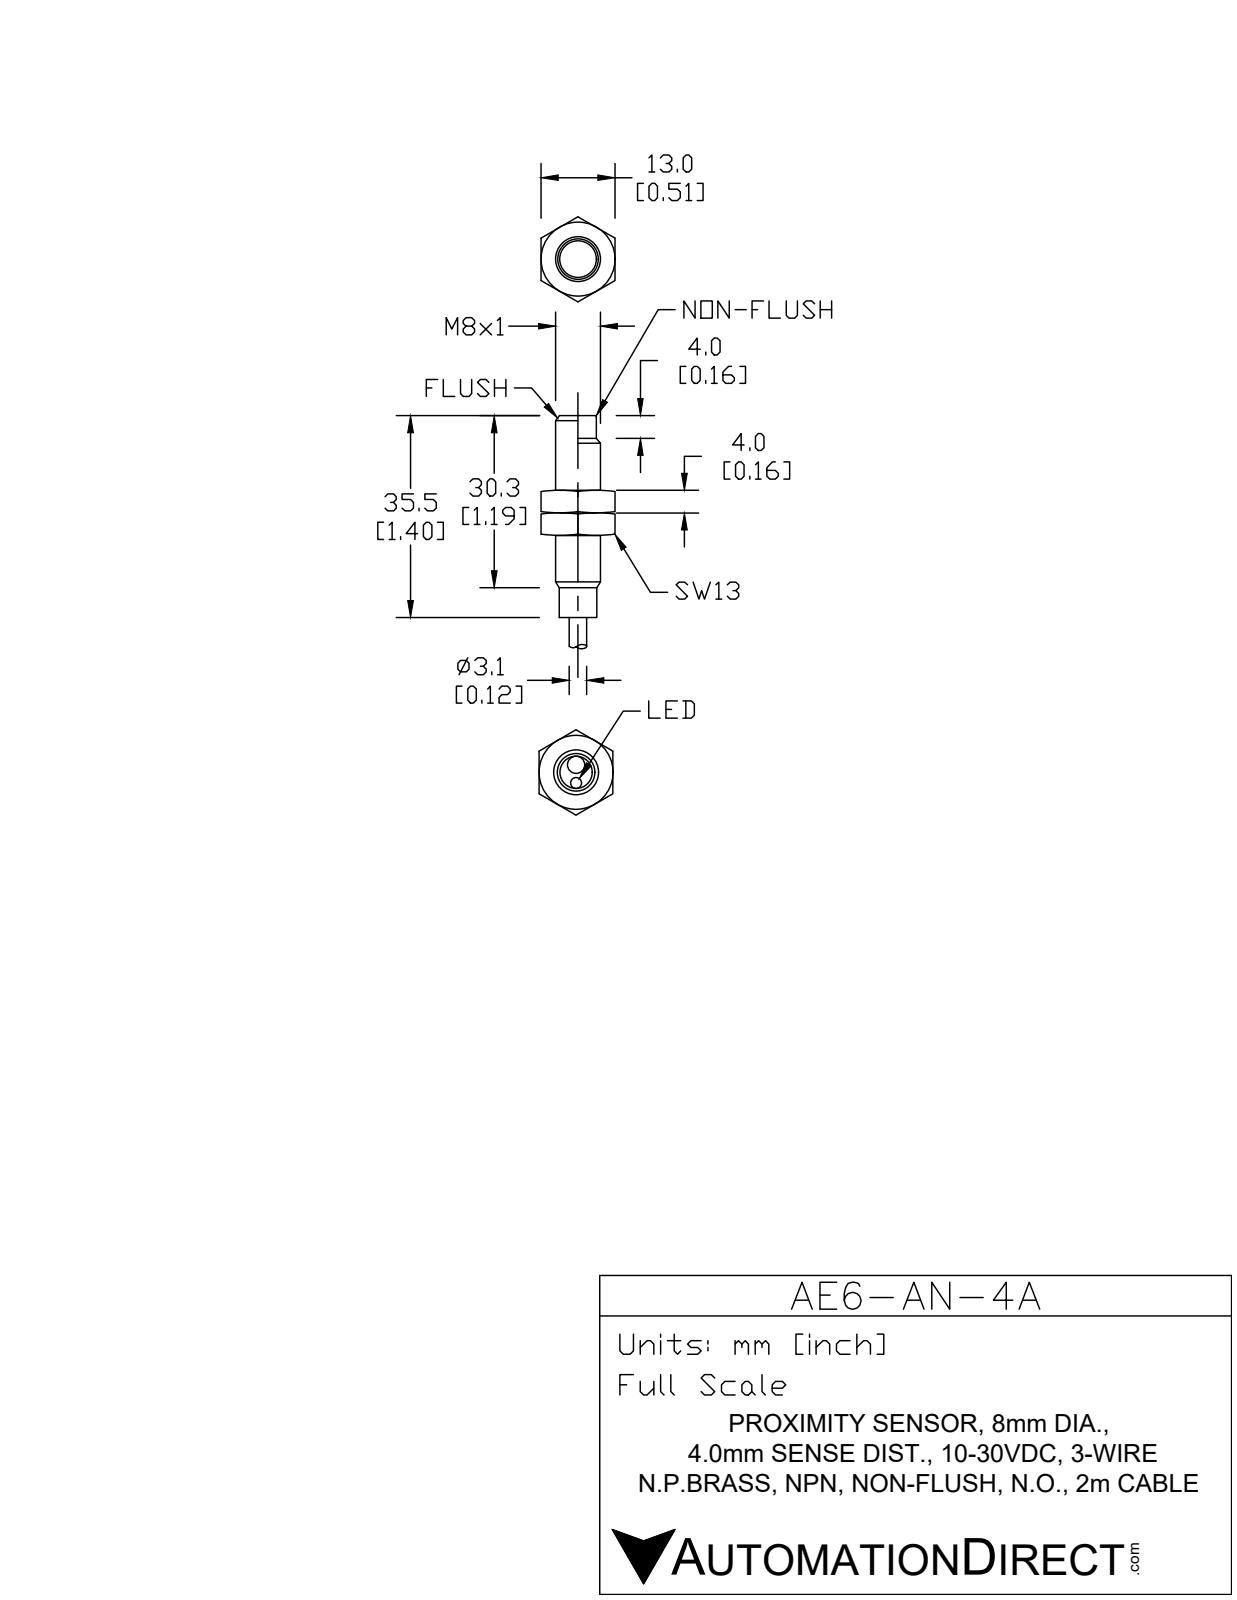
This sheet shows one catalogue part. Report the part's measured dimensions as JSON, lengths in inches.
{"part_name": "AE6-AN-4A", "step_written_by": "SolidWorks 2017 (AUTOMOTIVE_DESIGN)", "units": "inches", "bodies": {"solids": 4, "faces": 30, "planar": 10, "cylindrical": 12, "other": 8}, "overall_size": [2.933, 0.315, 0.315], "volume_in3": 0.116, "surface_area_in2": 2.281, "round_holes": [[0.122, 1], [0.228, 1]], "round_bosses_or_shafts": [[0.315, 1], [0.256, 1], [0.254, 1]], "face_to_face_distances": [1.031, 0.157, 1.189, 1.378, 1.22, 0.189, 0.02, 1.358, 1.201, 0.169], "hole_center_spacings": [0.045]}
